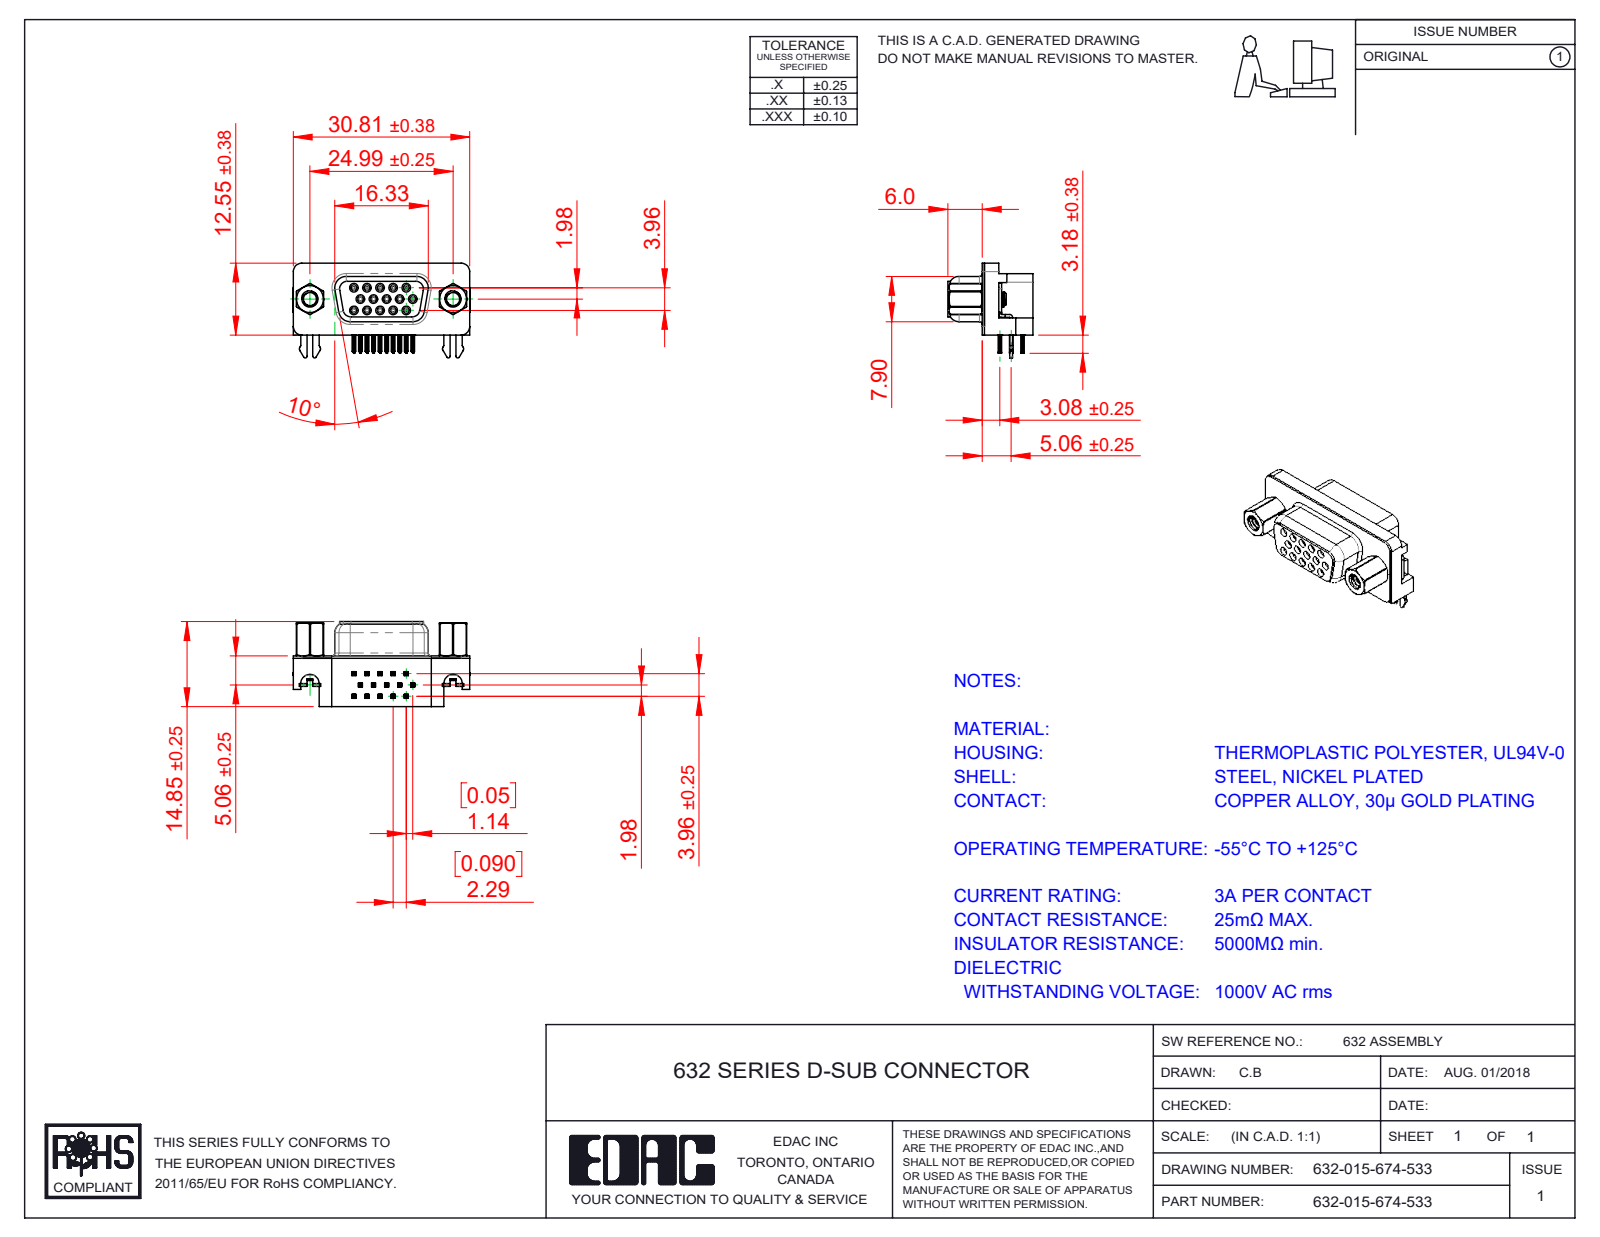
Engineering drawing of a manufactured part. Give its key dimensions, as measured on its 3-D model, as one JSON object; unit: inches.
{"part_name": "632 Contact Bottom; 632 Contact Top; 632 Contact Middle_Recessed; 632 4-40 Hex Standoff 5 (+5 more)", "step_written_by": "SolidWorks 2016 (CONFIG_CONTROL_DESIGN)", "units": "inches", "bodies": {"solids": 21, "faces": 2376, "planar": 996, "cylindrical": 646, "other": 734}, "overall_size": [1.216, 0.652, 0.585], "volume_in3": 0.186, "surface_area_in2": 8.024, "round_holes": [[0.031, 15], [0.035, 15], [0.09, 2], [0.157, 2], [0.189, 2], [0.197, 2]], "round_bosses_or_shafts": [[0.047, 15], [0.193, 2], [0.11, 2]], "partial_cylinders_radius": [[0.004, 120], [0.006, 60], [0.014, 30], [0.013, 15], [0.039, 11], [0.011, 10], [0.02, 10], [0.053, 8]], "face_to_face_distances": [0.016, 0.078, 0.333, 0.348, 0.114, 0.098, 0.234, 0.264, 0.278, 0.125], "hole_center_spacings": [0.09, 0.09, 0.156, 0.18, 0.238, 0.156, 0.18, 0.27]}
